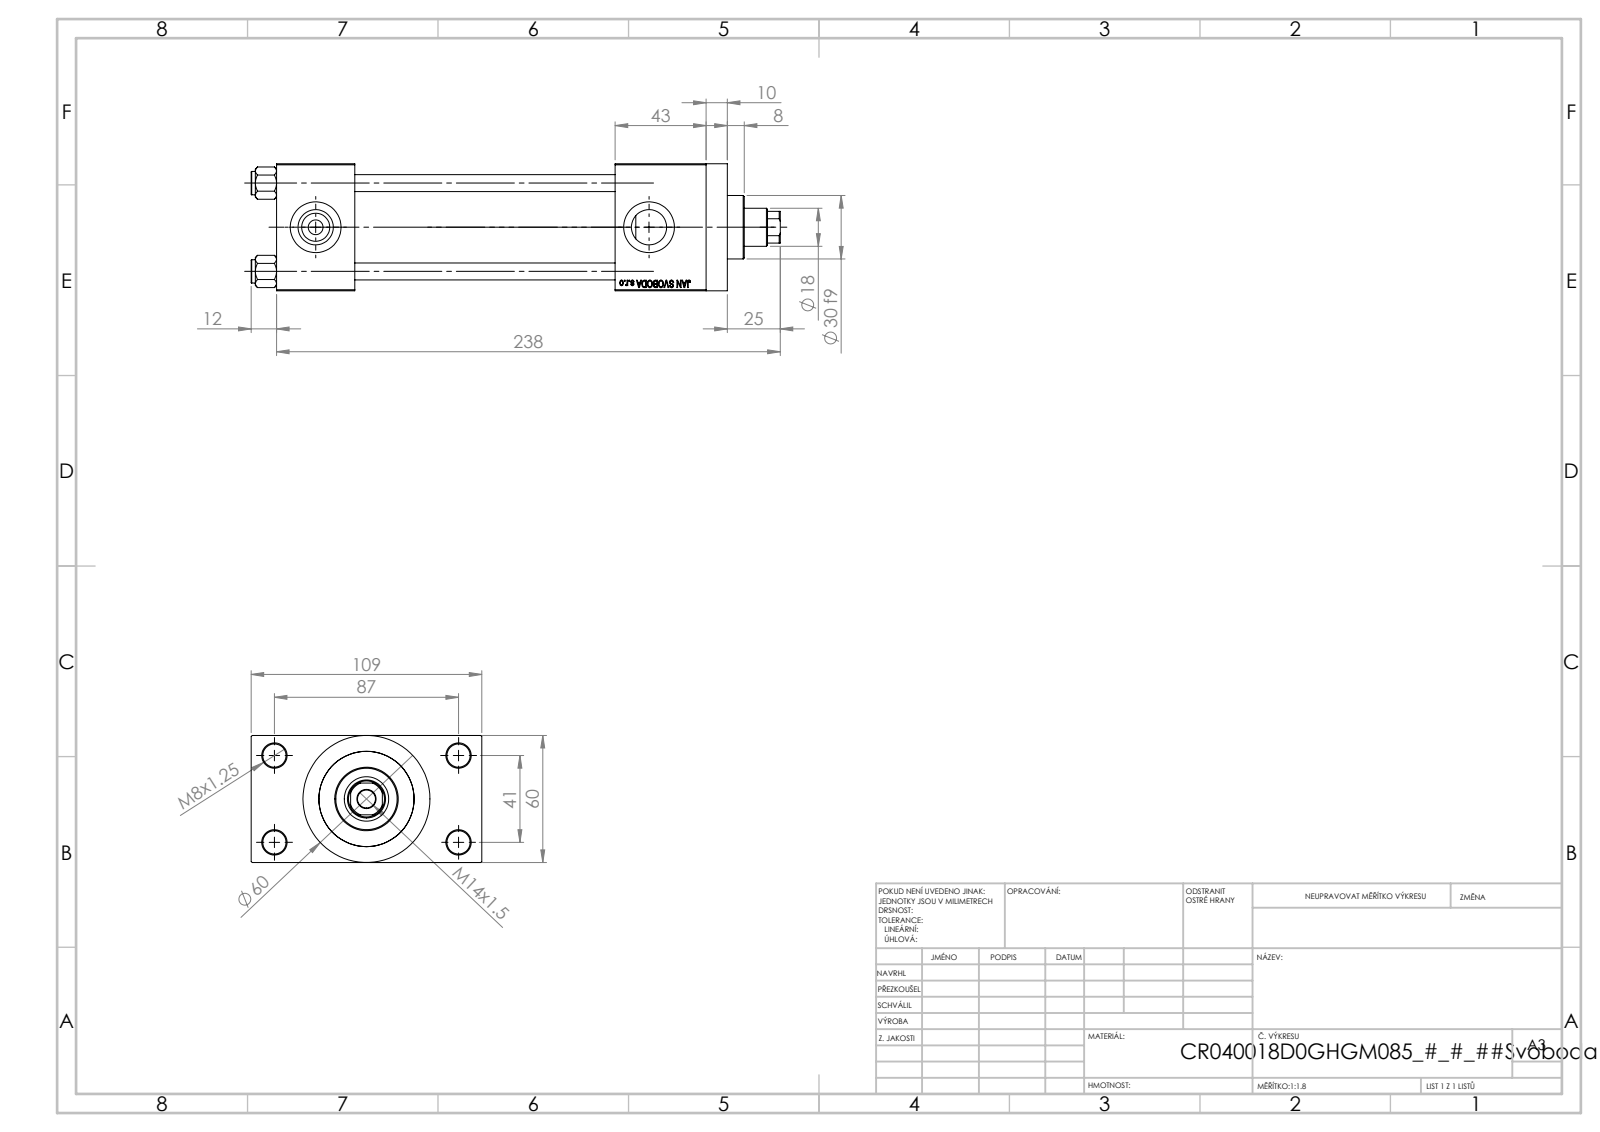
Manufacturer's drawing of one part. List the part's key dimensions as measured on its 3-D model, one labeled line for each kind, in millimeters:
Part name (STEP PRODUCT): V215CR_D_Body; NUT_M5_D; V215CR_VCP_D; V215_VC_A (+1 more)
STEP written by: SolidWorks 2019 (CONFIG_CONTROL_DESIGN)
Units: millimetres
Bodies: 11 solids, 1104 faces (498 planar, 88 cylindrical, 518 other)
Overall size (bounding box): 250 × 109 × 60
Volume: 568 474 mm³ · Surface area: 150 318 mm²
Round holes (diameter × count): ⌀8 ×4, ⌀11 ×4, ⌀7 ×2, ⌀16.66 ×2, ⌀24 ×2, ⌀8.5 ×1, ⌀18 ×1, ⌀21 ×1, ⌀31 ×1, ⌀40 ×1, ⌀45 ×1
Round bosses / shafts (diameter × count): ⌀11 ×4, ⌀60 ×1, ⌀46 ×1, ⌀30 ×1
Partial cylindrical surfaces — rounded edges, fillets, slot ends (radius × count): R8.5 ×1
Main face-to-face distances: 60, 123, 24.5, 84.5, 37, 160, 203, 166, 43, 10
Hole centre spacings: 22.65, 29.49, 41.7, 47.15, 48.09, 64.35, 76.49, 41
